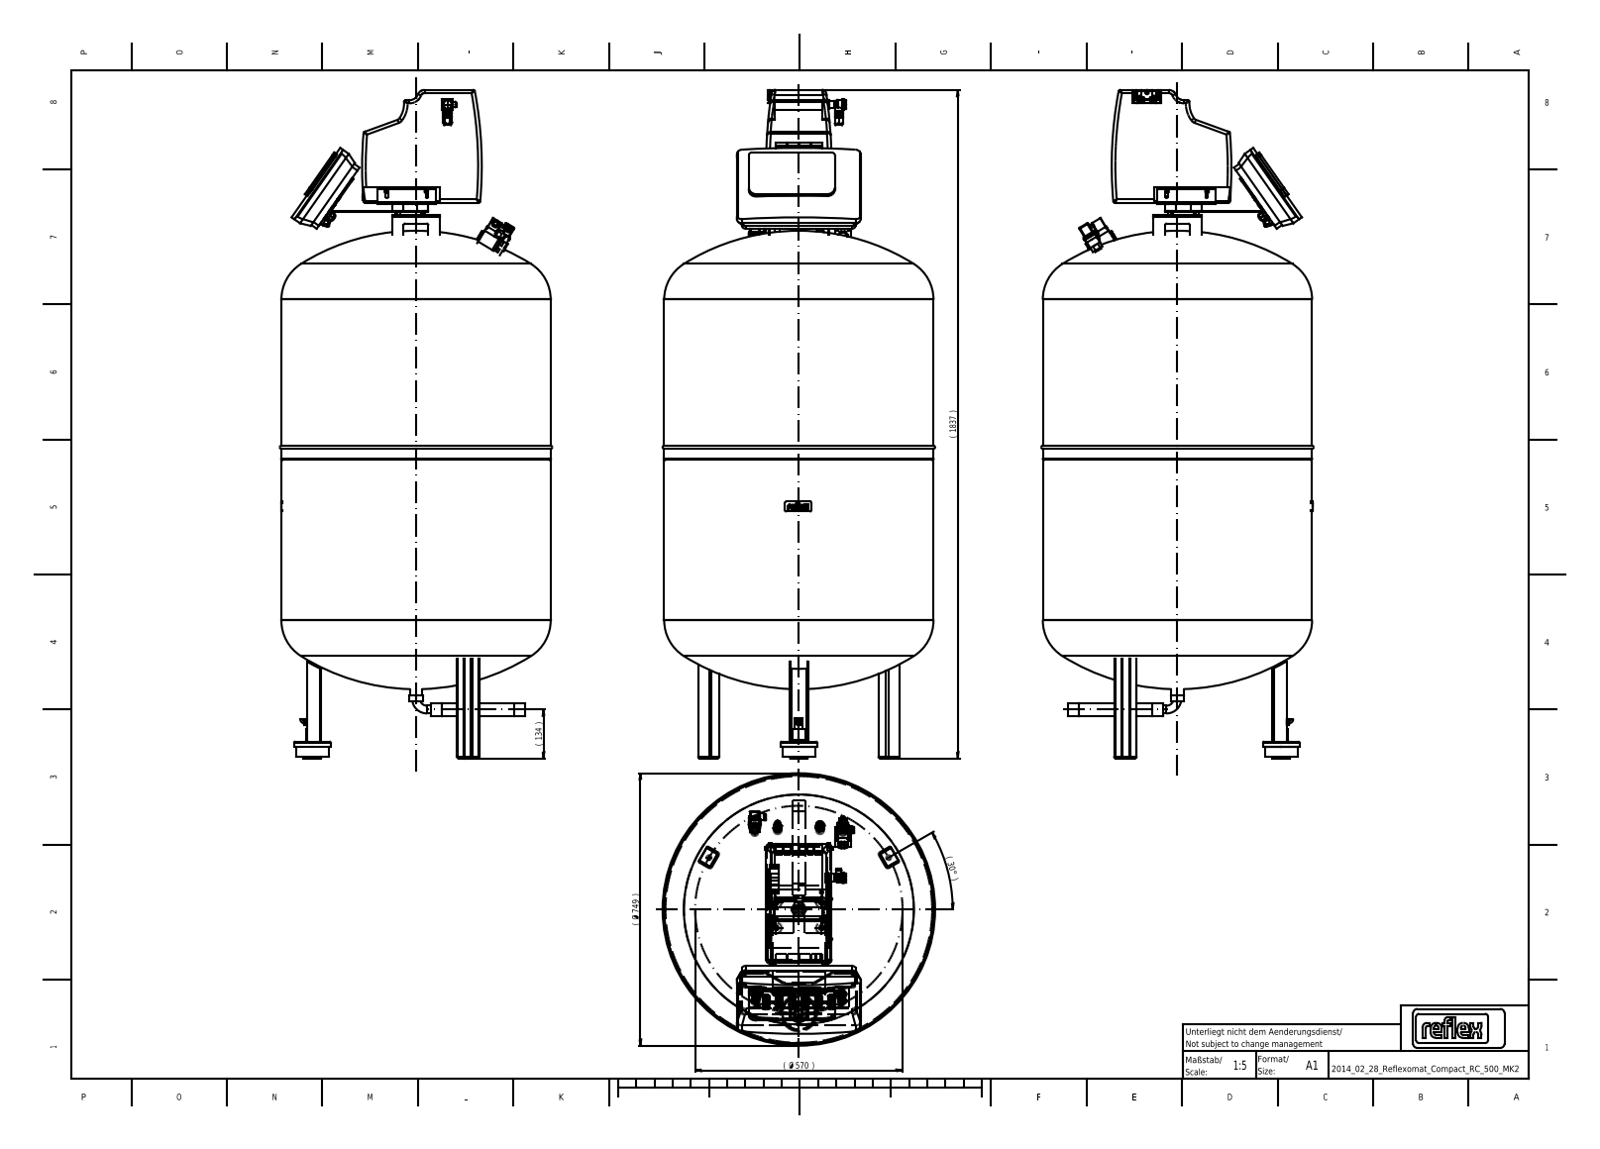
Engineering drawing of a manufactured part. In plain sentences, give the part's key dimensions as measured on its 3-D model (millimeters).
Its 3-D file was written by "Mechanical Desktop 2011 (CONFIG_CONTROL_DESIGN)". It is 42 solids with 2542 faces: 1705 planar, 419 cylindrical and 418 other. Overall it measures 1837 by 748.8 by 748.8 millimeters. Its volume is 507 400 000 cubic millimeters and its surface area 6 585 000 square millimeters. Round holes: 8 of diameter 8.2, 8 of diameter 10.5, 7 of diameter 17, 4 of diameter 5.5, 4 of diameter 9, 2 of diameter 10, 2 of diameter 13.4, 1 of diameter 2, 1 of diameter 6.5, 1 of diameter 7, 1 of diameter 14, 1 of diameter 20. Round bosses or shafts: 8 of diameter 19, 8 of diameter 16, 8 of diameter 8, 7 of diameter 17.5, 4 of diameter 30, 3 of diameter 21.3, 3 of diameter 19.8, 2 of diameter 35. Partial cylindrical surfaces (rounded edges, fillets, slot ends): 31 of radius 2.5, 23 of radius 5, 14 of radius 8, 11 of radius 10, 10 of radius 1, 6 of radius 3, 4 of radius 3.94, 4 of radius 4.5. The main face-to-face distances are 882, 4, 2.5, 22, 2, 47.5, 1148, 266, 26, 1126. The hole center spacings are 125, 36, 22, 70, 72, 125.14, 126.92, 128.1.
